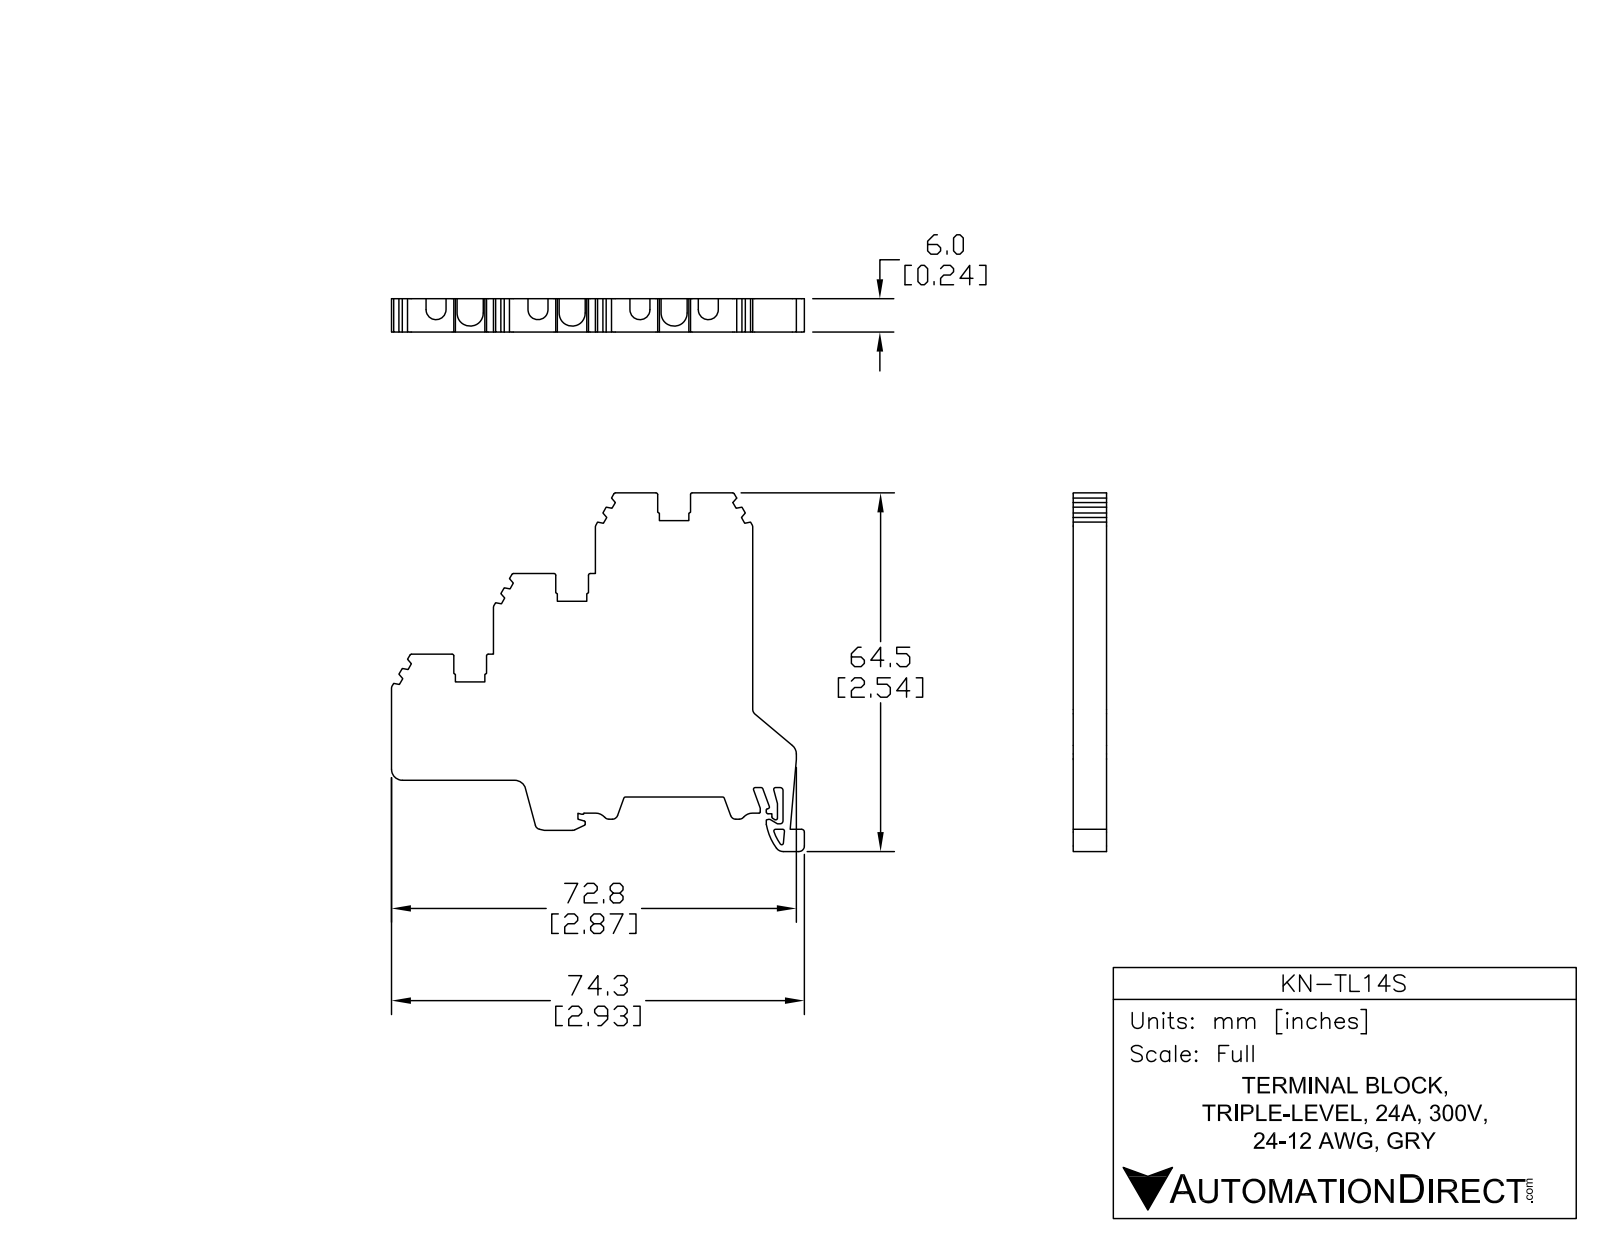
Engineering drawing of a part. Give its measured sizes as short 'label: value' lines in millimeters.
name: KN-TL14S
written by: SolidWorks 2014 (AUTOMOTIVE_DESIGN)
unit: mm
bodies: 1 solid, 217 faces (147 planar, 70 cylindrical, 0 other)
size: 74.3 × 64.51 × 6
volume: 16 268 mm³; area: 7 819 mm²
rounds: 23× R0.3, 8× R1, 7× R0.5, 6× R0.2, 4× R1.8, 4× R2, 3× R2.35, 2× R2.13
face distances: 6, 14.5, 18.35, 1, 3, 4, 54.7, 29, 5, 17.1
